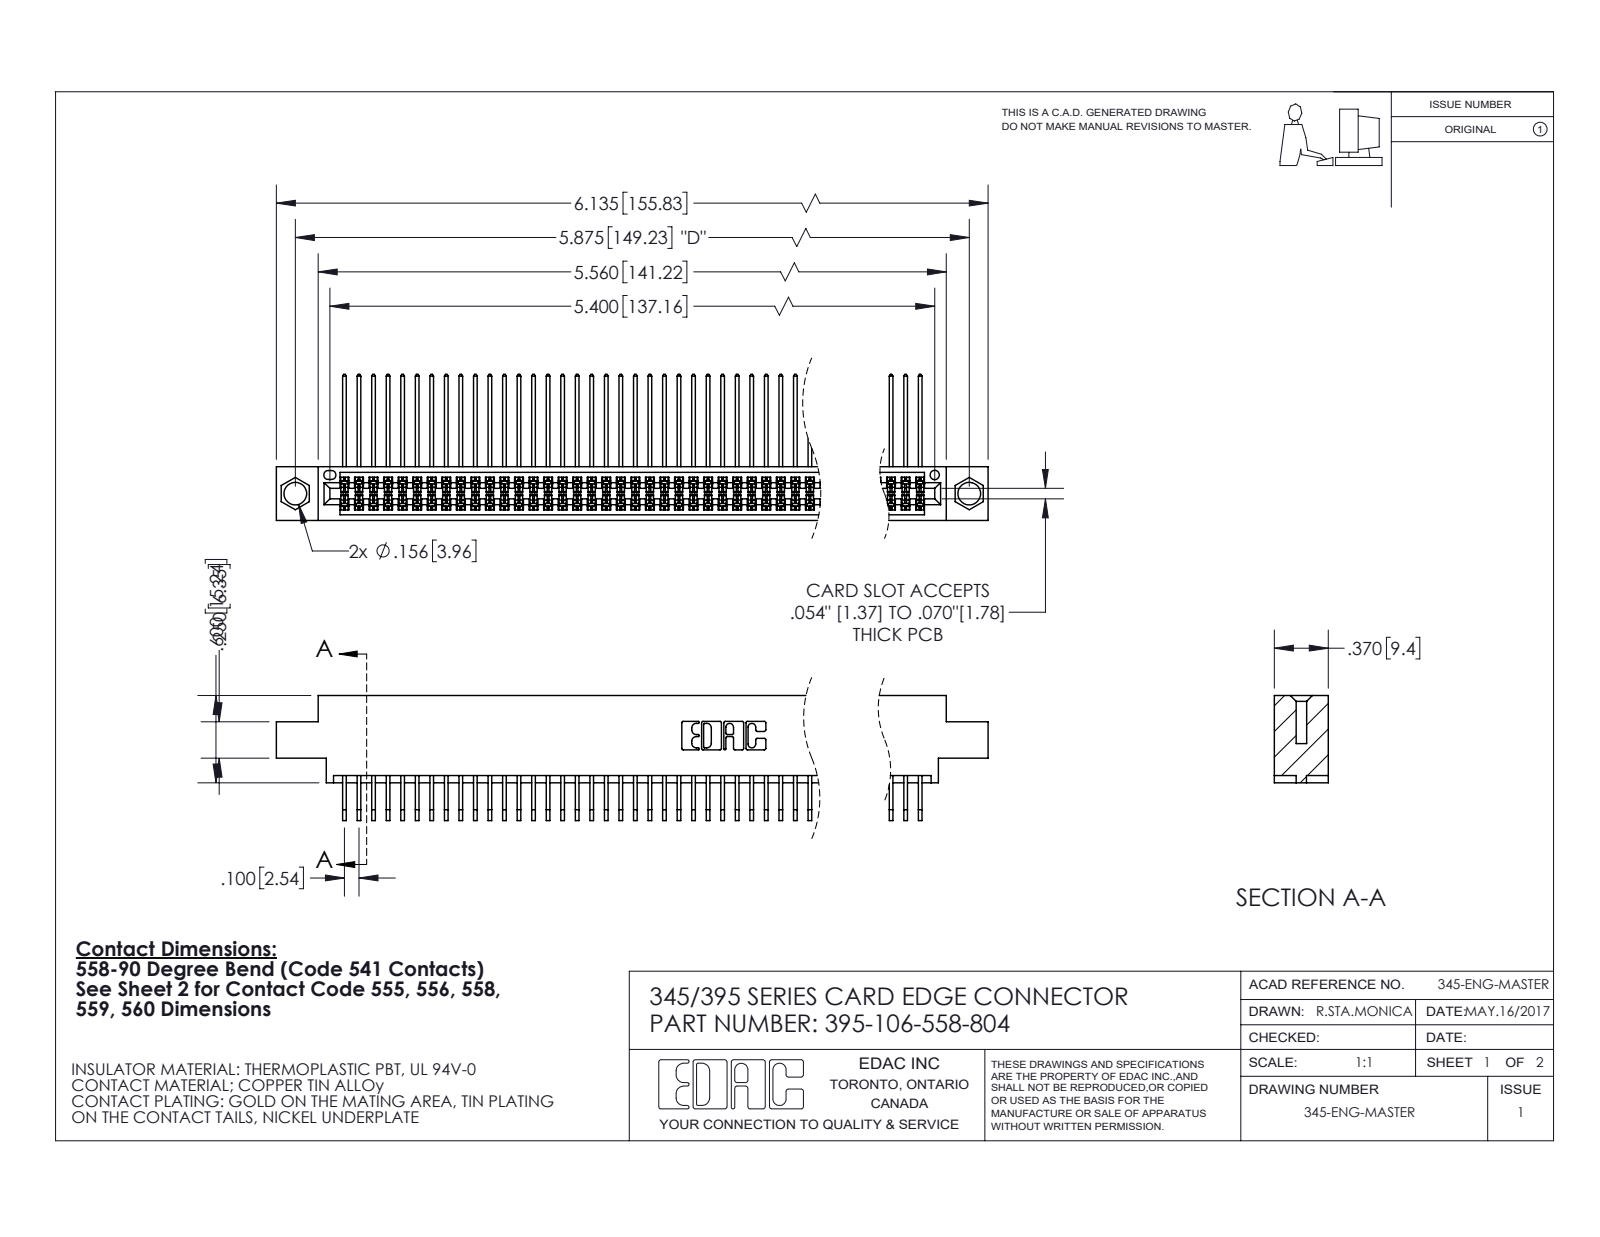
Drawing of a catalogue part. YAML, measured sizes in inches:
part_name: "395-106-558-804; 345-292-001_558 Tail - 2; 345-292-001_558 559 Tail - 1; 345 Part_0.170 Offset - 0.156 Dia-TI"
step_written_by: "SolidWorks 2020 (CONFIG_CONTROL_DESIGN)"
units: inches
bodies: {solids: 107, faces: 5656, planar: 3808, cylindrical: 1848, other: 0}
overall_size: [6.135, 1.005, 0.859]
volume: 0.954
surface_area: 40.59
round_holes:
  - {diameter: 0.156, count: 2}
  - {diameter: 0.064, count: 1}
partial_cylinders:
  - {radius: 0.006, count: 212}
  - {radius: 0.01, count: 22}
  - {radius: 0.007, count: 6}
  - {radius: 0.031, count: 6}
  - {radius: 0.026, count: 3}
  - {radius: 0.014, count: 2}
  - {radius: 0.019, count: 2}
  - {radius: 0.022, count: 2}
face_to_face_distances: [0.072, 0.298, 0.2, 0.37, 0.098, 0.272, 0.025, 0.225, 0.175, 0.025]
hole_center_spacings: [0.27, 5.639, 5.875]
